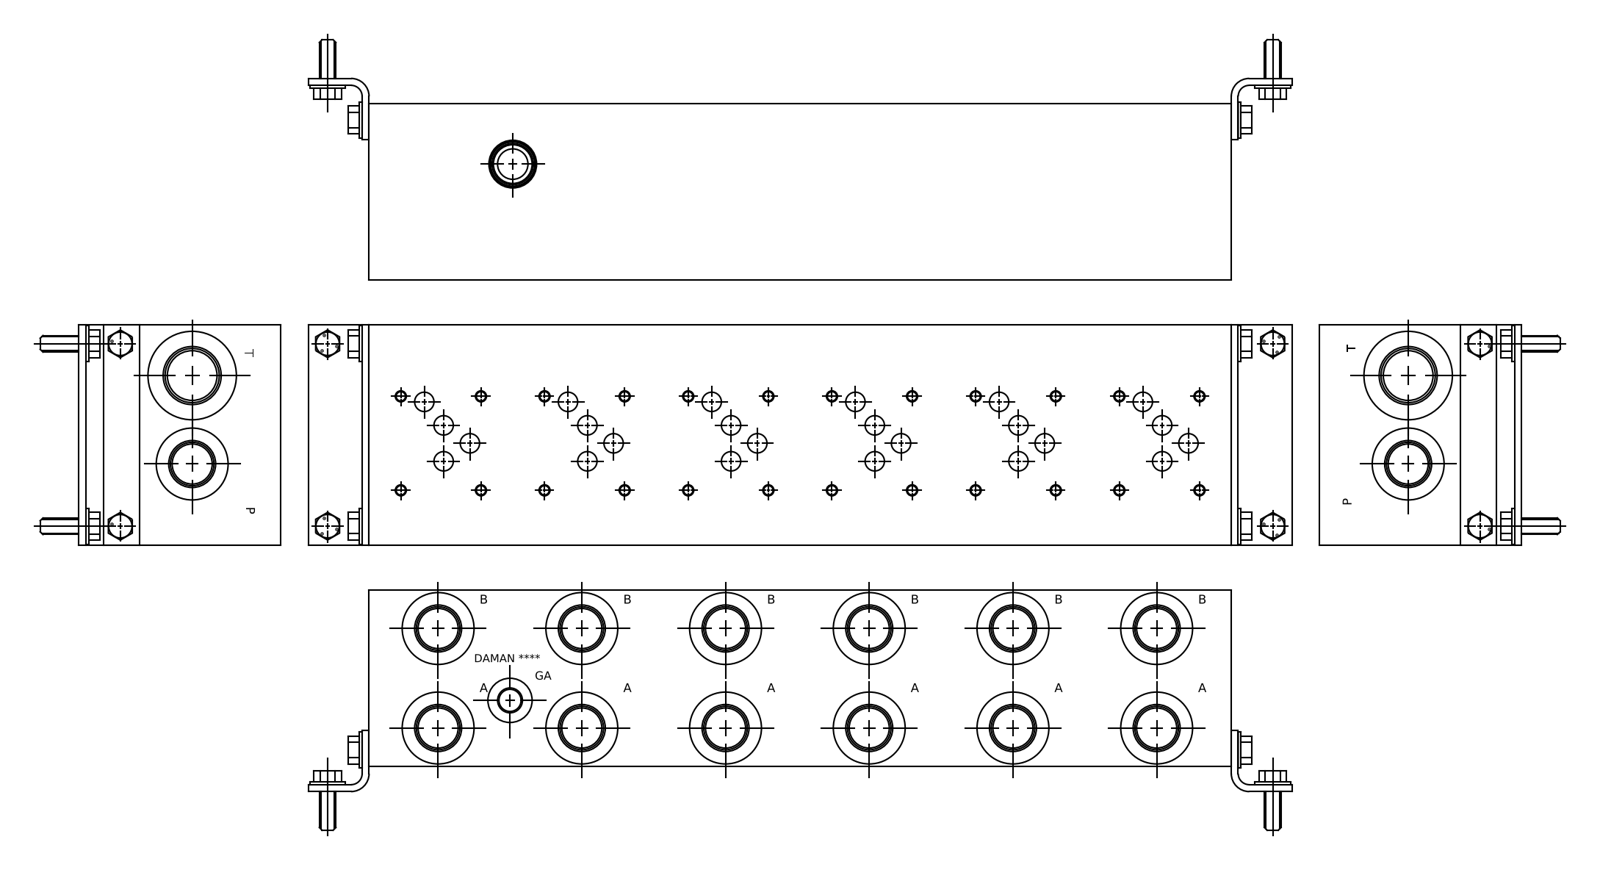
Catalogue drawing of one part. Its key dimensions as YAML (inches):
part_name: "Part_AD05HP063S~S_3D"
step_written_by: "Autodesk Inventor 2019 (AUTOMOTIVE_DESIGN)"
units: inches
bodies: {solids: 1, faces: 1055, planar: 512, cylindrical: 173, other: 370}
overall_size: [19.5, 5, 4]
volume: 366.9
surface_area: 493
round_holes:
  - {diameter: 0.201, count: 24}
  - {diameter: 0.25, count: 24}
  - {diameter: 0.438, count: 22}
  - {diameter: 0.906, count: 13}
  - {diameter: 0.981, count: 13}
  - {diameter: 1.08, count: 13}
  - {diameter: 1.655, count: 13}
  - {diameter: 1.063, count: 12}
  - {diameter: 0.312, count: 2}
  - {diameter: 0.375, count: 2}
  - {diameter: 0.437, count: 2}
  - {diameter: 1.063, count: 2}
face_to_face_distances: [4, 5, 0.031, 19.5, 4.969, 19.469, 0.75, 19.438, 0.781, 4.219]
hole_center_spacings: [3.25, 6.5, 9.75, 0.719, 2.687, 3.953, 13, 3.35]
